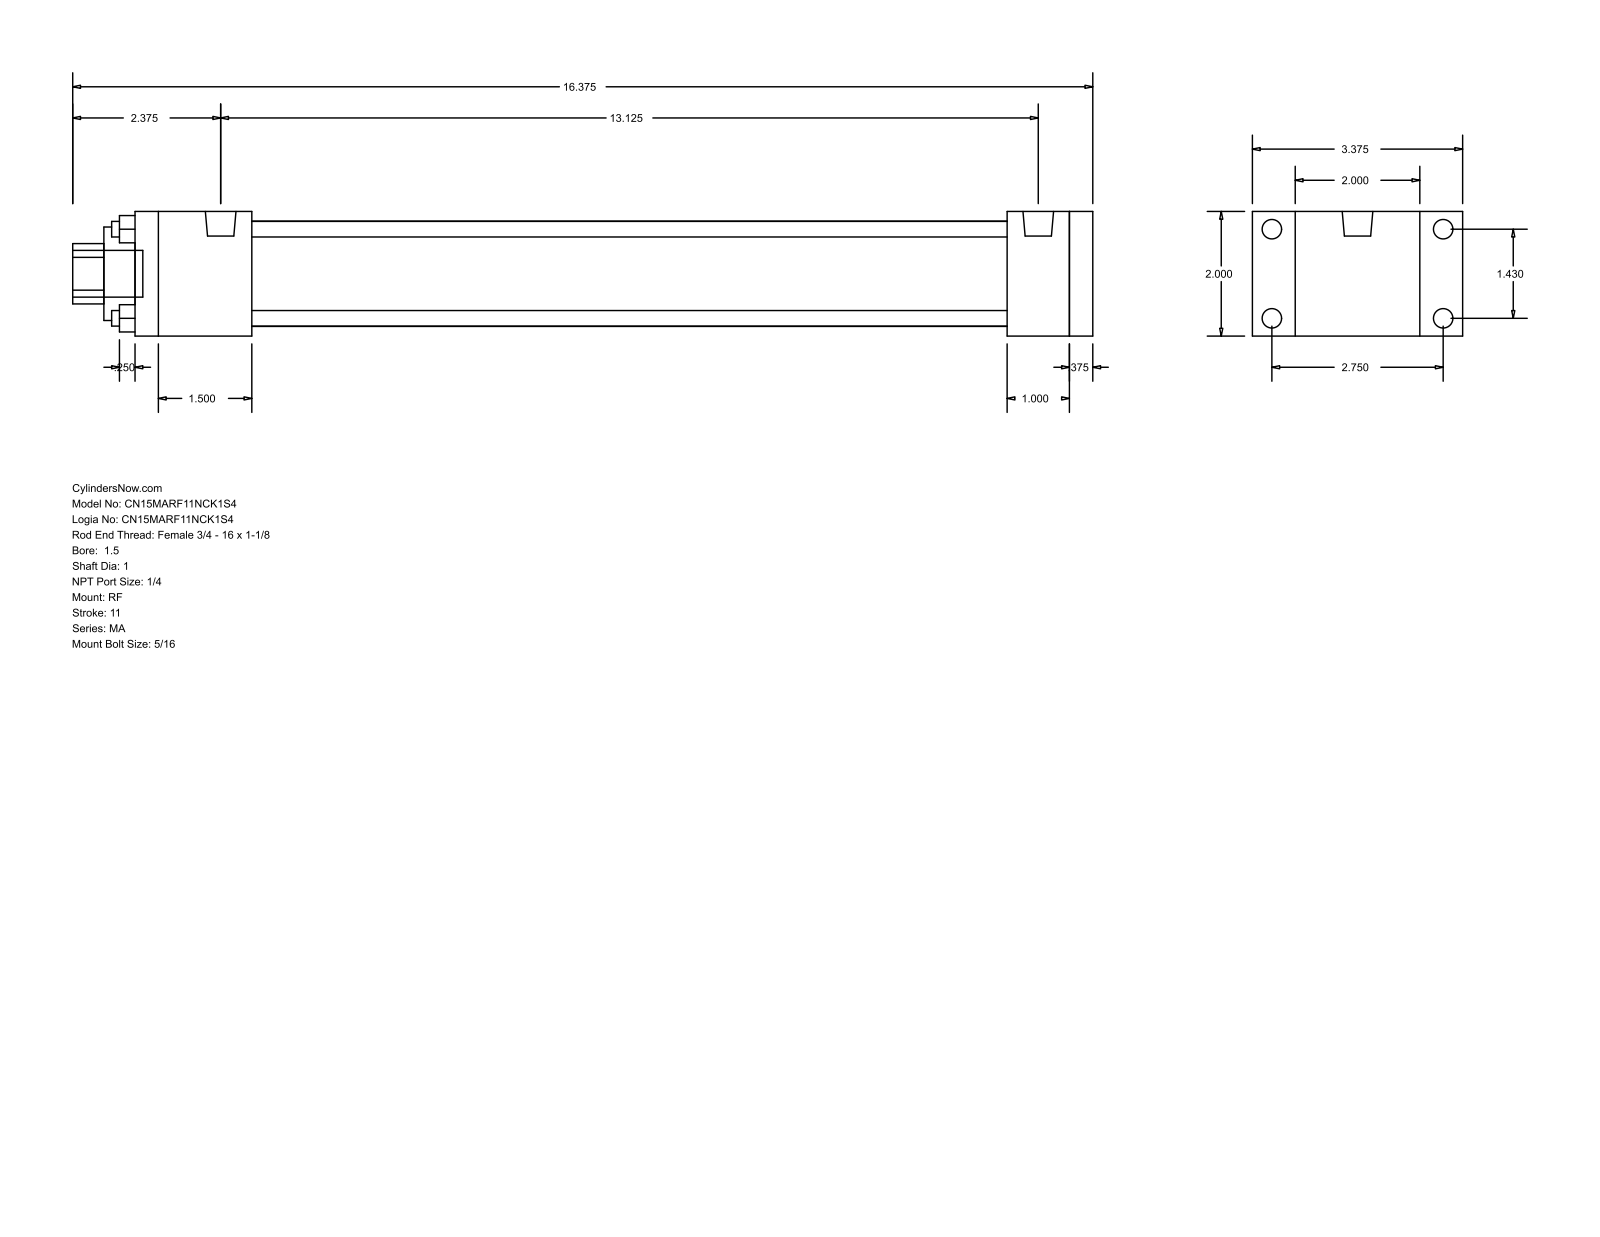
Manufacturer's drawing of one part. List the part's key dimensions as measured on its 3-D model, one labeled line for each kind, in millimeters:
Part name (STEP PRODUCT): MA_RF__0150_1
STEP written by: GSSL Pune (CONFIG_CONTROL_DESIGN)
Units: millimetres
Bodies: 0 solids, 92 faces (64 planar, 28 cylindrical, 0 other)
Overall size (bounding box): 415.93 × 85.72 × 50.8
Round holes (diameter × count): ⌀6.35 ×4, ⌀25.4 ×1, ⌀38.1 ×1, ⌀42.93 ×1
Round bosses / shafts (diameter × count): ⌀7.94 ×8, ⌀12.49 ×2, ⌀19.05 ×1
Partial cylindrical surfaces — rounded edges, fillets, slot ends (radius × count): R12.29 ×1
Main face-to-face distances: 50.8, 9.53, 381, 25.4, 390.53, 355.6, 34.93, 47.63, 307.97, 333.37
Hole centre spacings: 25.68, 36.32, 51.36
